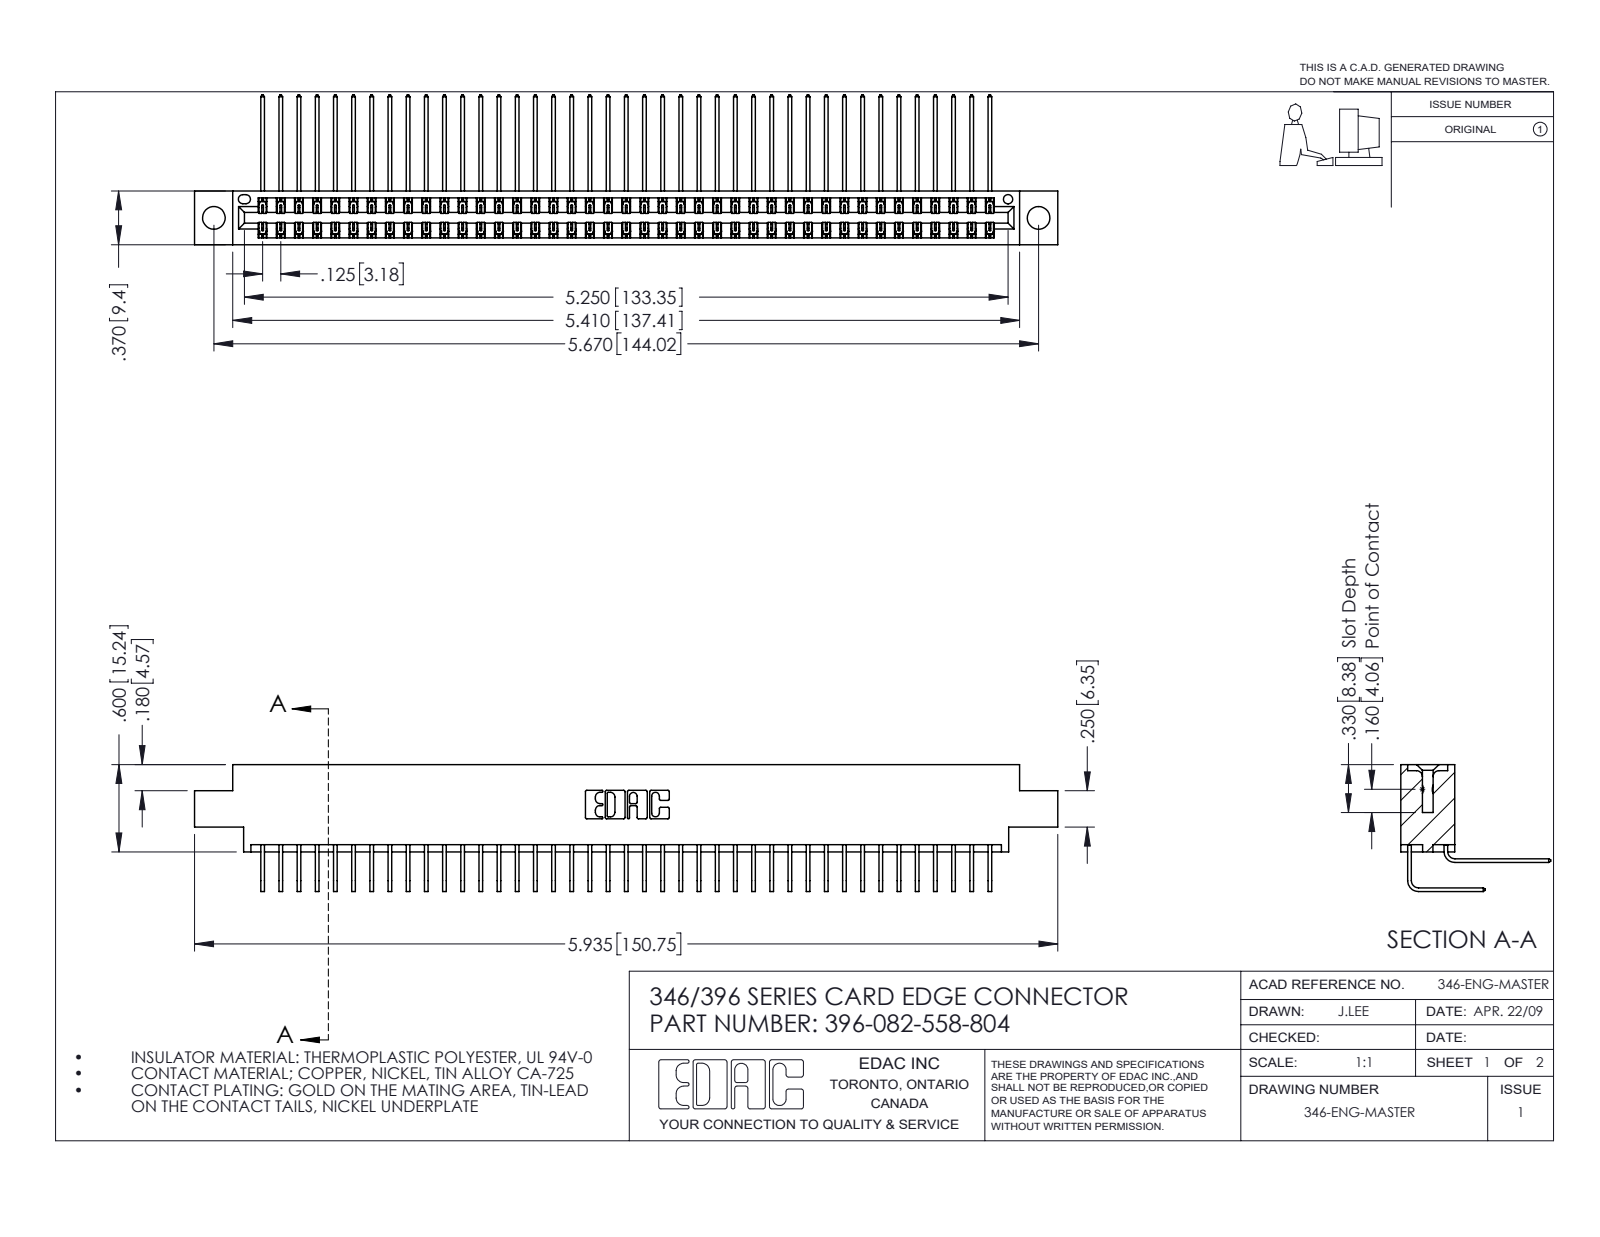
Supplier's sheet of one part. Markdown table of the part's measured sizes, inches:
| quantity | value |
| --- | --- |
| part name | 396-082-558-804; 346 Part_0.170 Offset - 0.156 Dia-TH; 345-292-001_558 559 Tail - 1; 345-292-001_558 Tail - 2 |
| STEP written by | SolidWorks 2016 (CONFIG_CONTROL_DESIGN) |
| units | inches |
| bodies | 83 solids, 4554 faces (3114 planar, 1440 cylindrical, 0 other) |
| overall size | 5.935 × 1.03 × 0.873 |
| volume | 0.911 in³ |
| surface area | 35.28 in² |
| round holes (diameter × count) | 0.156 × 2, 0.064 × 1 |
| partial cylindrical surfaces (radius × count) | 0.006 × 123, 0.01 × 22, 0.007 × 6, 0.031 × 6, 0.026 × 3, 0.014 × 2, 0.022 × 2, 0.024 × 2 |
| main face-to-face distances | 0.322, 0.048, 0.025, 0.37, 0.25, 0.298, 0.072, 0.275, 0.148, 0.222 |
| hole center spacings | 0.246, 5.461, 5.67 |
